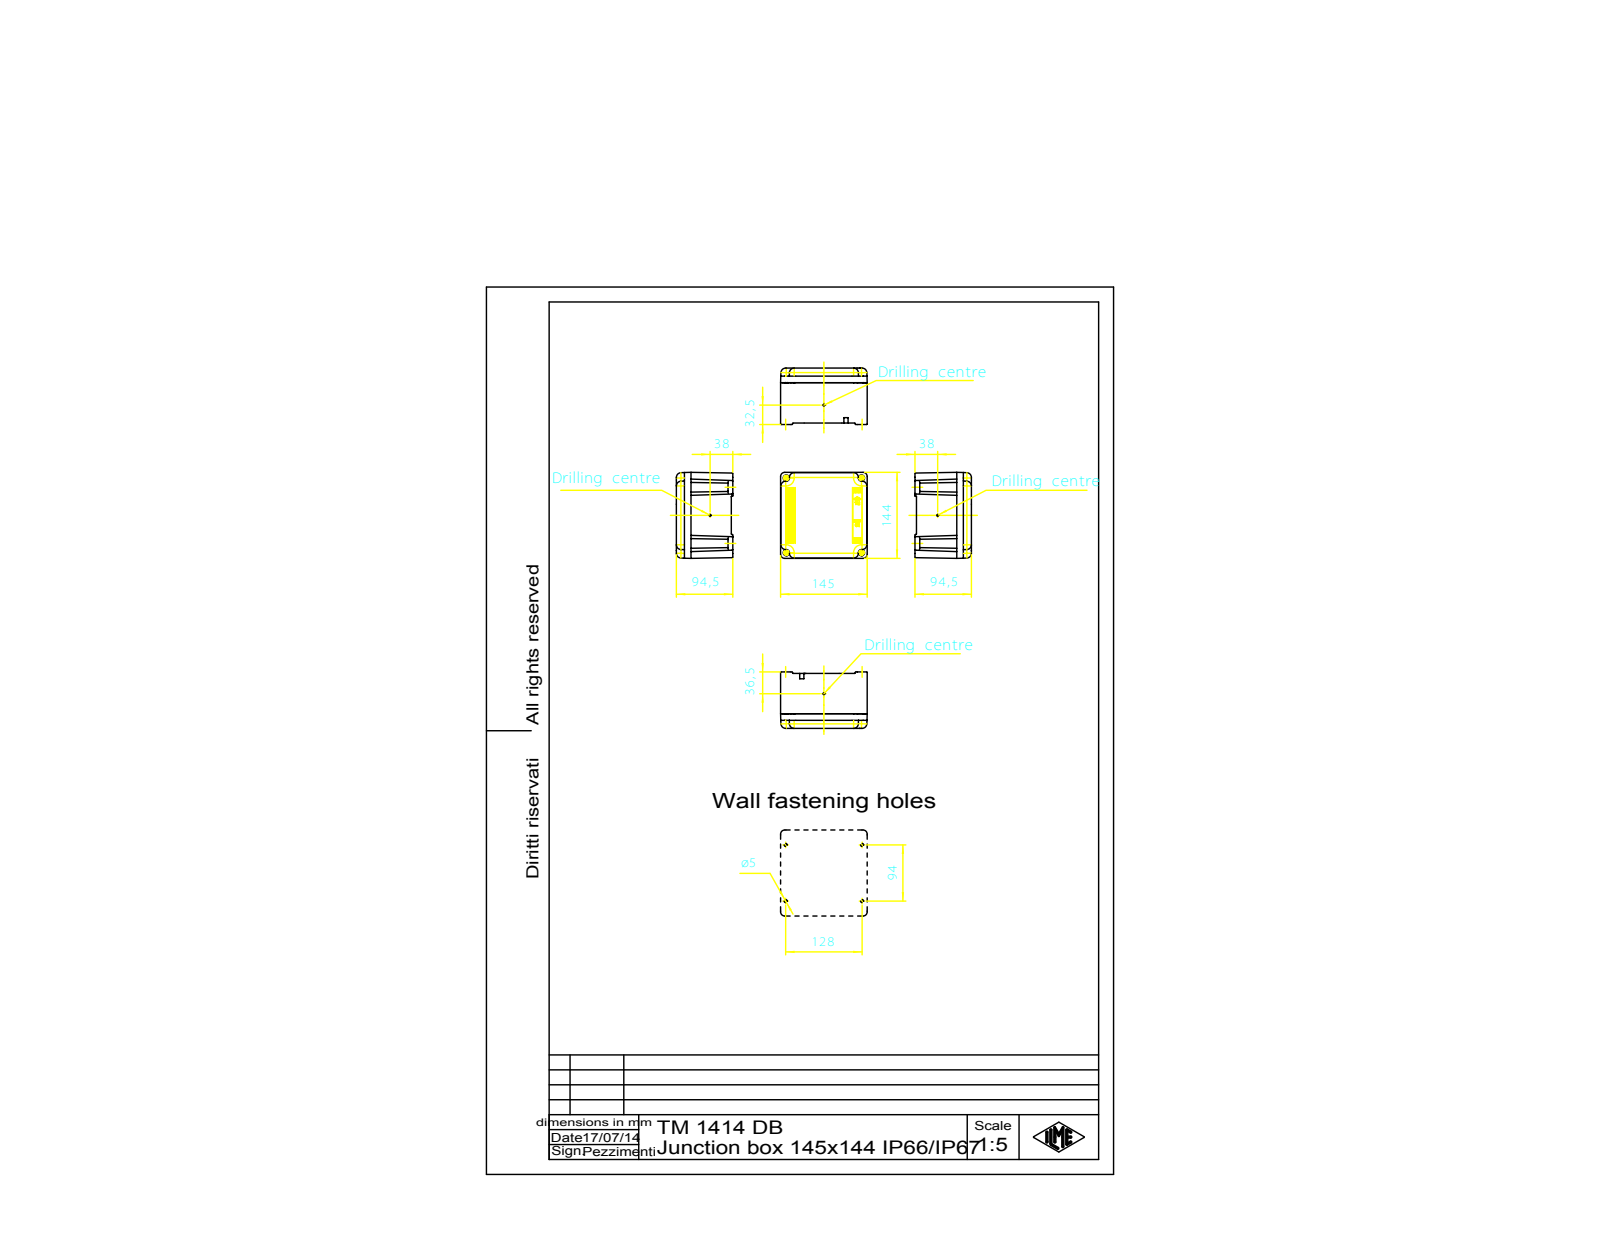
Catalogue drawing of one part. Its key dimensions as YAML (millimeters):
part_name: "COPERCHIO_1414; SCATOLA_1414; TM_1414_DB"
step_written_by: "Creo Elements/Direct Modeling 20.5B 27-May-2023 (C) Parametric Technology GmbH (AUTOMOTIVE_DESIGN)"
units: millimeters
bodies: {solids: 2, faces: 1047, planar: 763, cylindrical: 206, other: 78}
overall_size: [145, 144, 94.9]
volume: 500051
surface_area: 191610
round_holes:
  - {diameter: 5.2, count: 4}
round_bosses_or_shafts:
  - {diameter: 8.5, count: 4}
  - {diameter: 5, count: 4}
partial_cylinders:
  - {radius: 0.2, count: 80}
  - {radius: 3.5, count: 16}
  - {radius: 8, count: 16}
  - {radius: 0.25, count: 11}
  - {radius: 2.7, count: 8}
  - {radius: 3, count: 8}
  - {radius: 7, count: 8}
  - {radius: 9.5, count: 8}
face_to_face_distances: [87, 5, 92, 82, 3.99, 62.5, 67.5, 19.5, 24.5, 15.46]
hole_center_spacings: [125, 126, 177.49]
